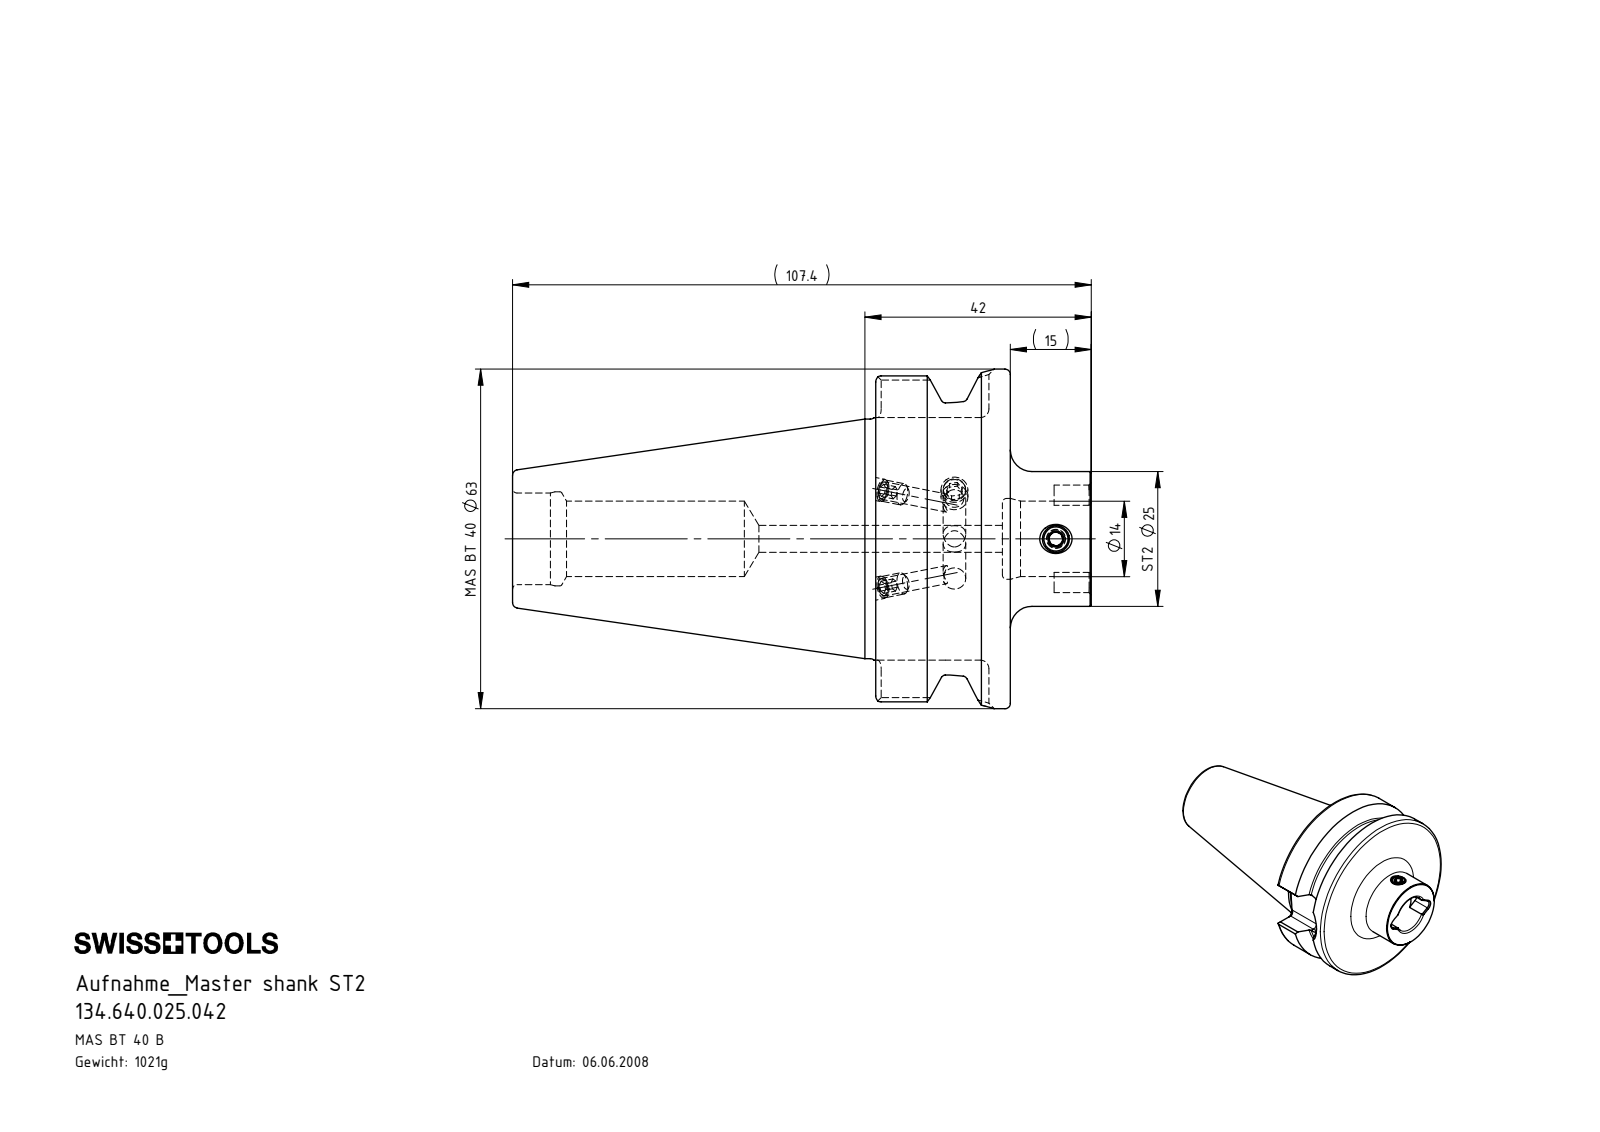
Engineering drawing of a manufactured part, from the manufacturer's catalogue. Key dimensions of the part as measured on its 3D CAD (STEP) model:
Part name (STEP PRODUCT): BB4-ST2.K01.042; ISO 4026 - M5 x 5_PreviewCfg; ST2-ER1.001.006_A; BB4-ST2.K01.042_A_mit Bundkhlung
STEP written by: SolidWorks 2015 (CONFIG_CONTROL_DESIGN)
Units: millimetres
Bodies: 3 solids, 170 faces (45 planar, 55 cylindrical, 70 other)
Overall size (bounding box): 107.4 × 63 × 63
Volume: 129 842 mm³ · Surface area: 23 961 mm²
Round holes (diameter × count): ⌀4 ×2, ⌀4.2 ×1, ⌀4.5 ×1, ⌀5 ×1, ⌀14 ×1, ⌀15 ×1, ⌀17 ×1, ⌀17.45 ×1
Round bosses / shafts (diameter × count): ⌀5 ×2, ⌀63 ×1, ⌀53 ×1, ⌀44.45 ×1, ⌀25 ×1
Partial cylindrical surfaces — rounded edges, fillets, slot ends (radius × count): R1.6 ×8, R1.8 ×2, R8.05 ×1
Main face-to-face distances: 25, 40, 15, 45, 67.4, 92.4, 107.4, 90.9, 23.5, 1.5
